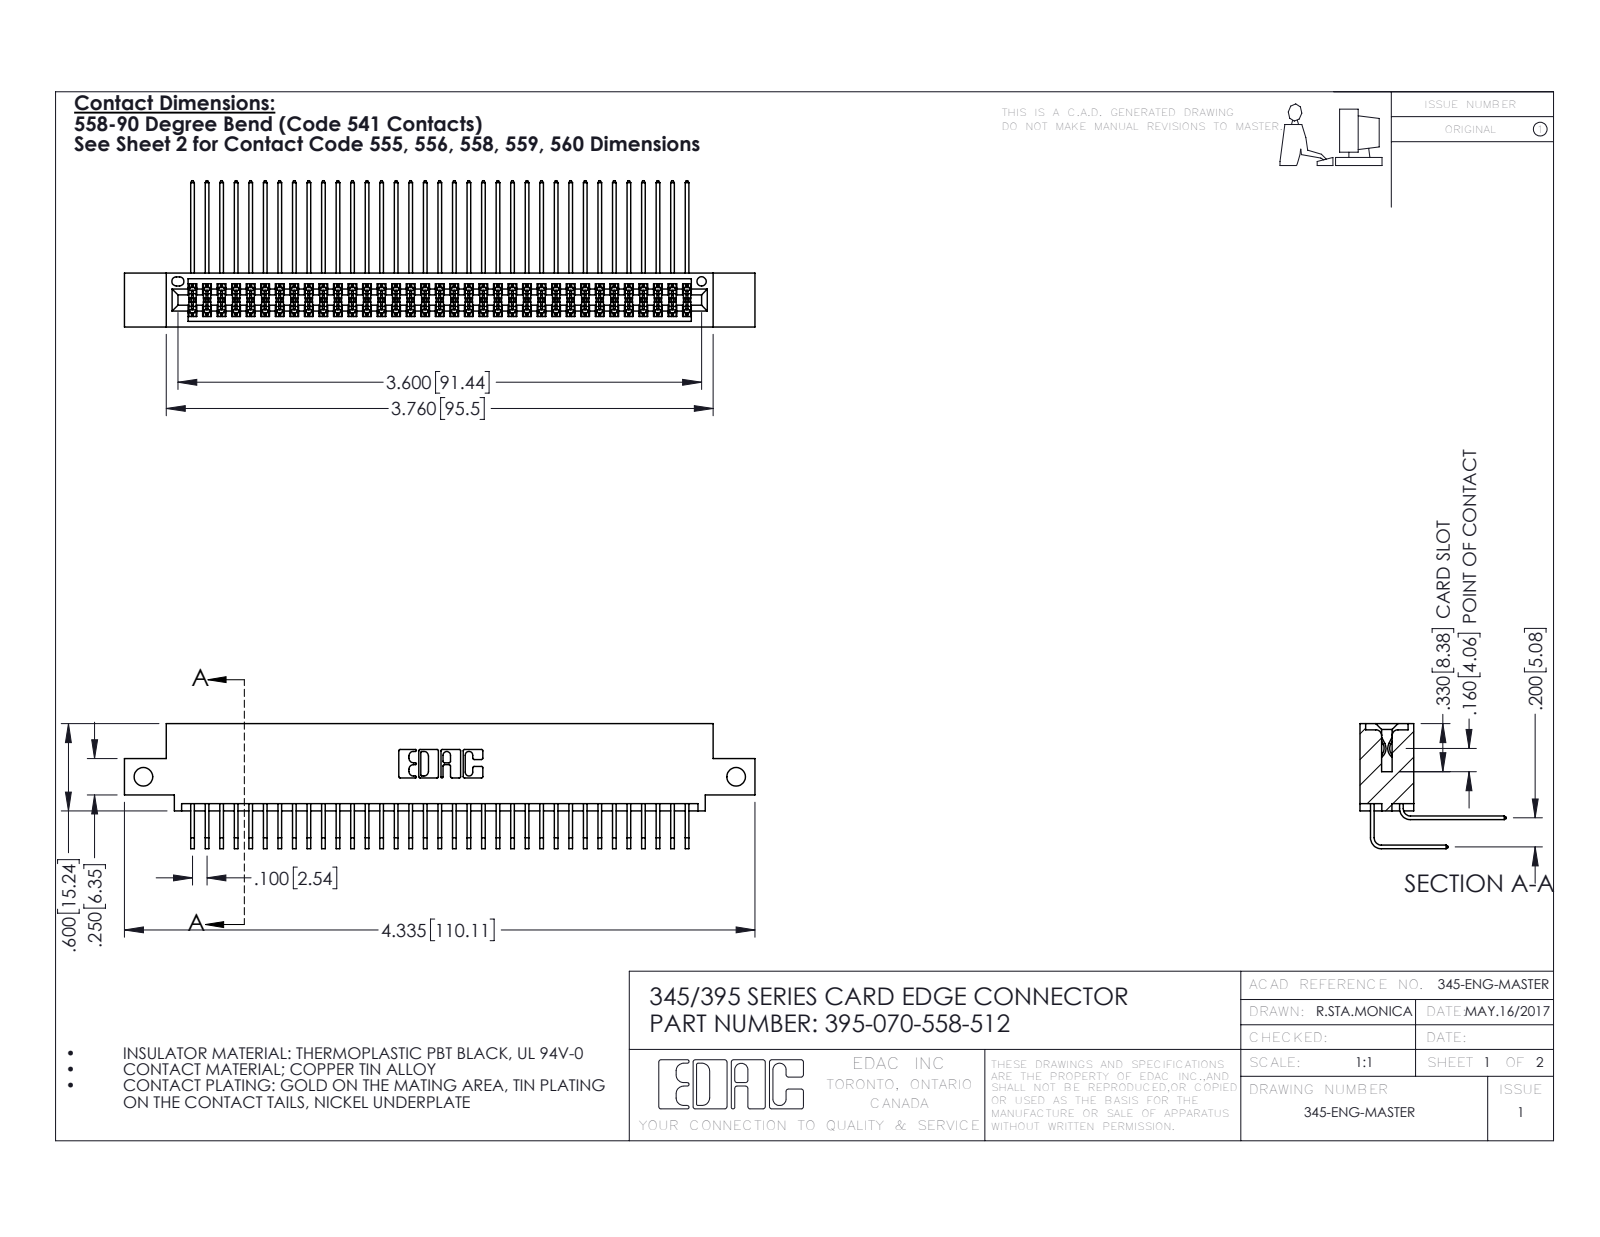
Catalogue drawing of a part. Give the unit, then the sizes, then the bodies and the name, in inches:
Units: inches
Overall size (bounding box): 4.335 × 1.005 × 0.859
Round holes (diameter × count): ⌀0.128 ×2, ⌀0.064 ×1
Partial cylindrical surfaces — rounded edges, fillets, slot ends (radius × count): R0.006 ×106, R0.01 ×22, R0.007 ×6, R0.031 ×6, R0.026 ×3, R0.014 ×2, R0.019 ×2, R0.022 ×2
Main face-to-face distances: 0.072, 0.298, 0.2, 0.37, 0.098, 0.272, 0.025, 0.225, 0.025, 0.175
Hole centre spacings: 4.075
Volume: 0.664 in³ · Surface area: 27.58 in²
Bodies: 71 solids, 3770 faces (2534 planar, 1236 cylindrical, 0 other)
Part name (STEP PRODUCT): 345 Part_0.110 Offset - Side Mount; 345-292-001_558 559 Tail - 1; 345-292-001_558 Tail - 2; 395-070-558-512
STEP written by: SolidWorks 2016 (CONFIG_CONTROL_DESIGN)
